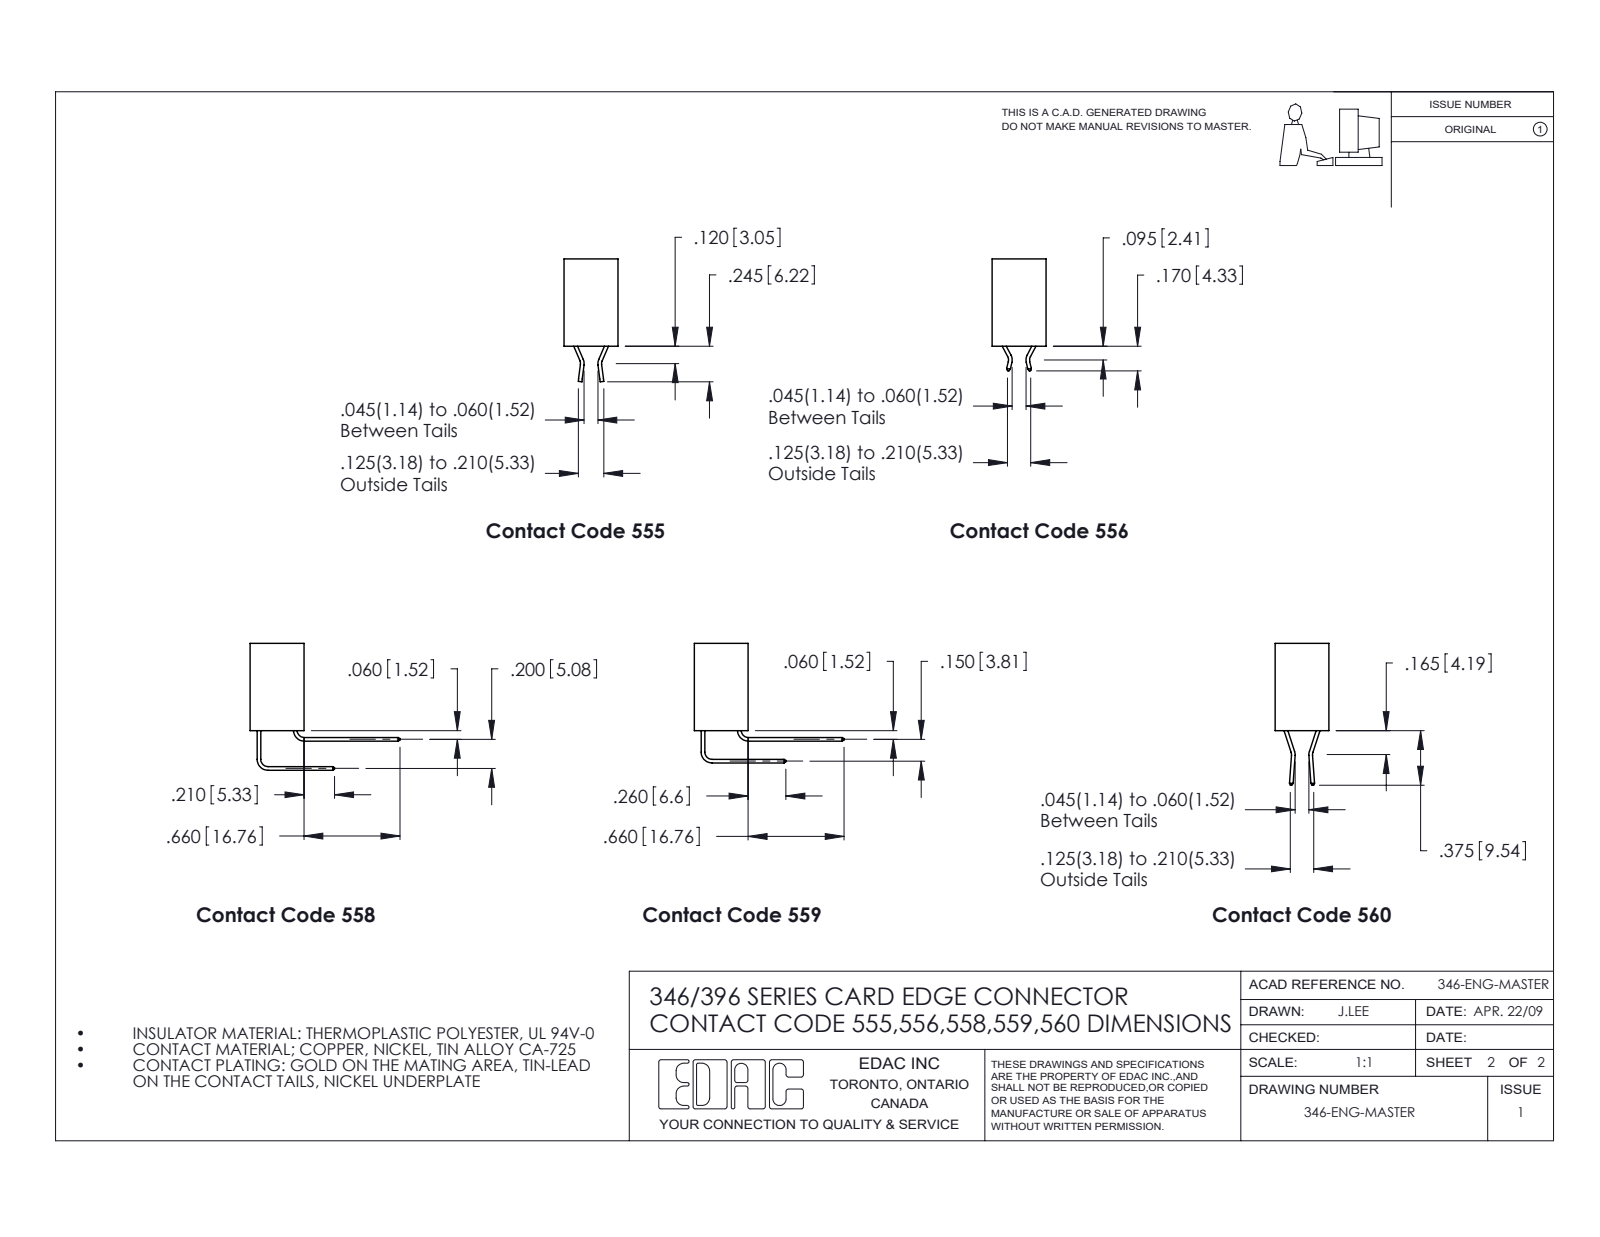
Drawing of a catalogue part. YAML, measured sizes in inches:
part_name: "346-220-058_345-220-058; 345-250-001_345-250-001-102; 345-292-001_558 Tail - 2; 346-058-558-858 (+2 more)"
step_written_by: "SolidWorks 2020 (CONFIG_CONTROL_DESIGN)"
units: inches
bodies: {solids: 63, faces: 3528, planar: 2388, cylindrical: 1080, other: 60}
overall_size: [4.966, 3.443, 1.03]
volume: 1.212
surface_area: 36.55
round_holes:
  - {diameter: 0.089, count: 2}
  - {diameter: 0.125, count: 2}
  - {diameter: 0.156, count: 2}
  - {diameter: 0.064, count: 1}
round_bosses_or_shafts:
  - {diameter: 0.155, count: 2}
partial_cylinders:
  - {radius: 0.006, count: 87}
  - {radius: 0.01, count: 22}
  - {radius: 0.06, count: 16}
  - {radius: 0.007, count: 6}
  - {radius: 0.031, count: 6}
  - {radius: 0.026, count: 3}
  - {radius: 0.014, count: 2}
  - {radius: 0.022, count: 2}
face_to_face_distances: [0.37, 0.322, 0.048, 0.072, 0.025, 0.148, 0.15, 0.298, 0.25, 0.275]
hole_center_spacings: [0.246, 3.962, 4.17]
